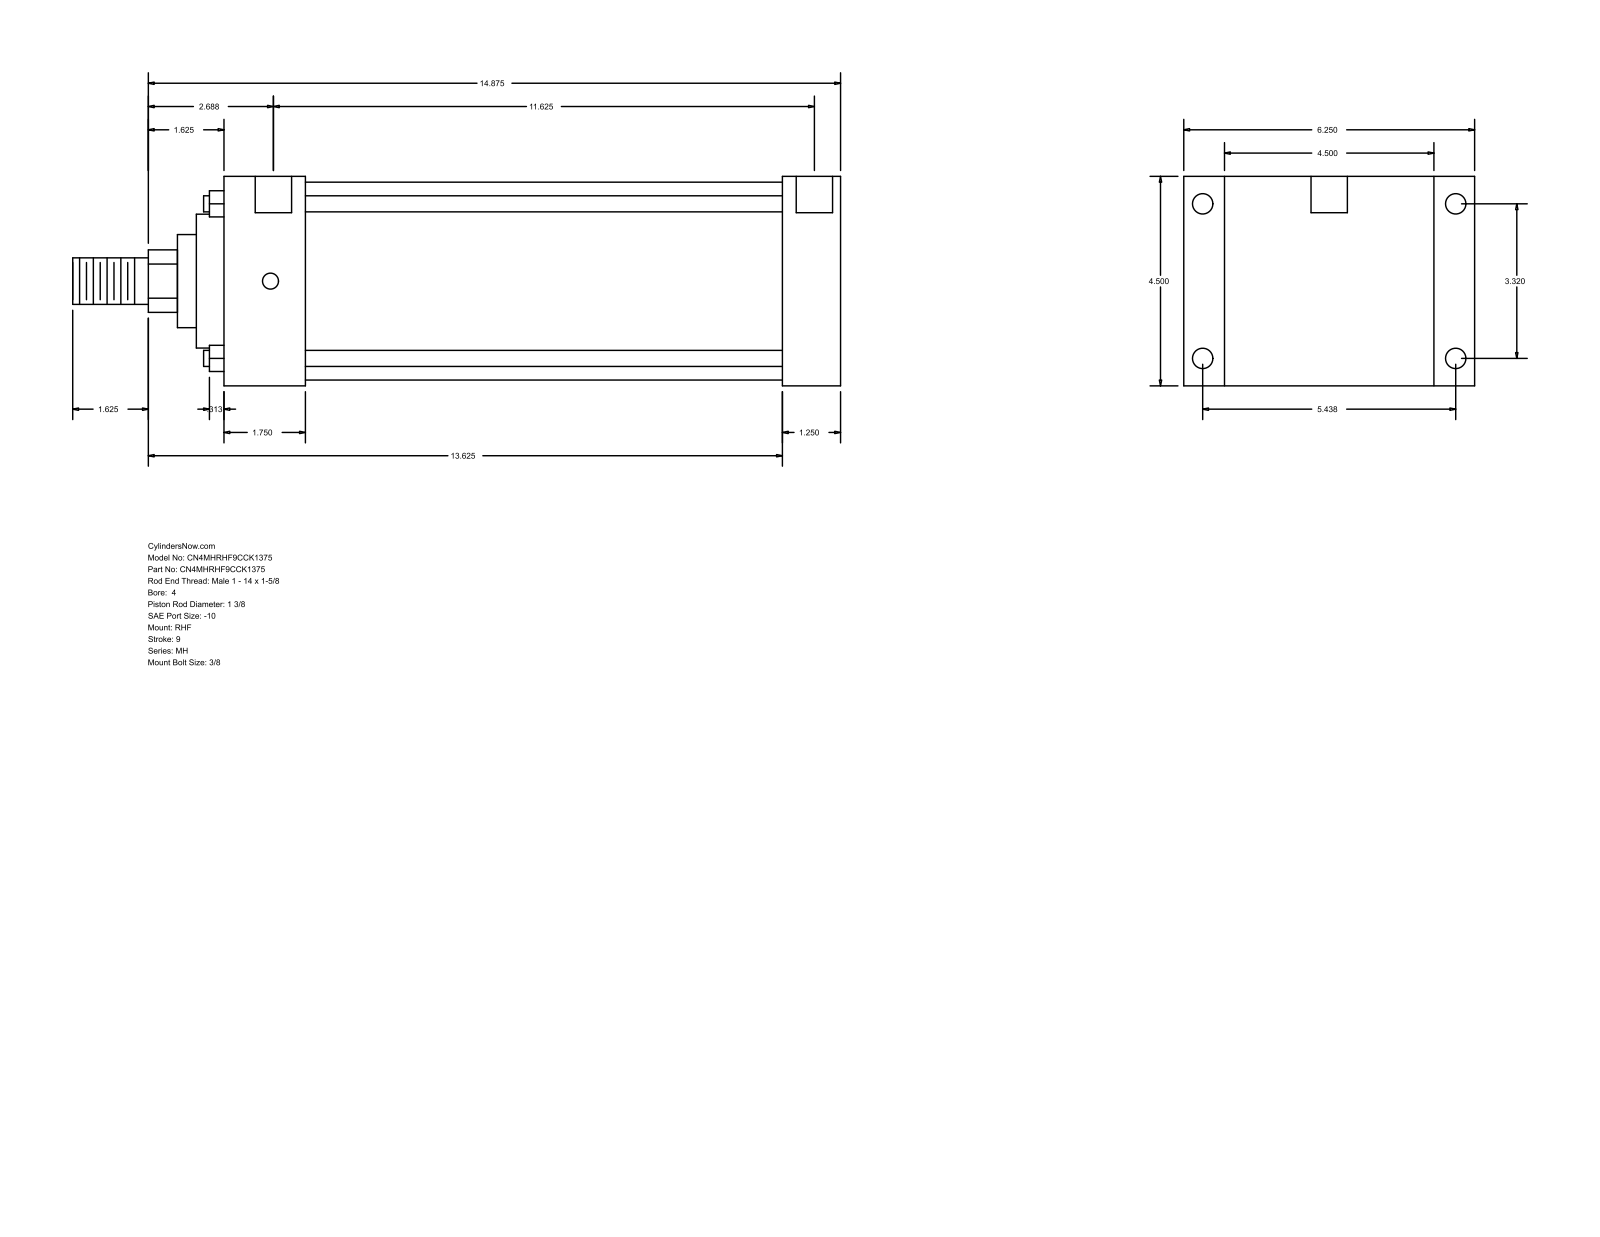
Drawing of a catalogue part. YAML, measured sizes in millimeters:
part_name: "MH_RHF__0400_1.375"
step_written_by: "GSSL Pune (CONFIG_CONTROL_DESIGN)"
units: millimeters
bodies: {solids: 0, faces: 90, planar: 61, cylindrical: 29, other: 0}
overall_size: [419.1, 158.75, 114.3]
round_holes:
  - {diameter: 8.73, count: 4}
  - {diameter: 11.13, count: 4}
  - {diameter: 19.84, count: 2}
round_bosses_or_shafts:
  - {diameter: 8.76, count: 4}
  - {diameter: 107.95, count: 1}
  - {diameter: 73.03, count: 1}
  - {diameter: 50.8, count: 1}
  - {diameter: 34.92, count: 1}
  - {diameter: 25.4, count: 1}
partial_cylinders:
  - {radius: 17.06, count: 1}
face_to_face_distances: [114.3, 31.75, 304.8, 336.55, 22.23, 136.53, 44.45, 260.35, 292.1, 158.76]
hole_center_spacings: [84.32, 138.12, 161.82, 298.45, 1.58, 1.59, 295.28, 296.86]
